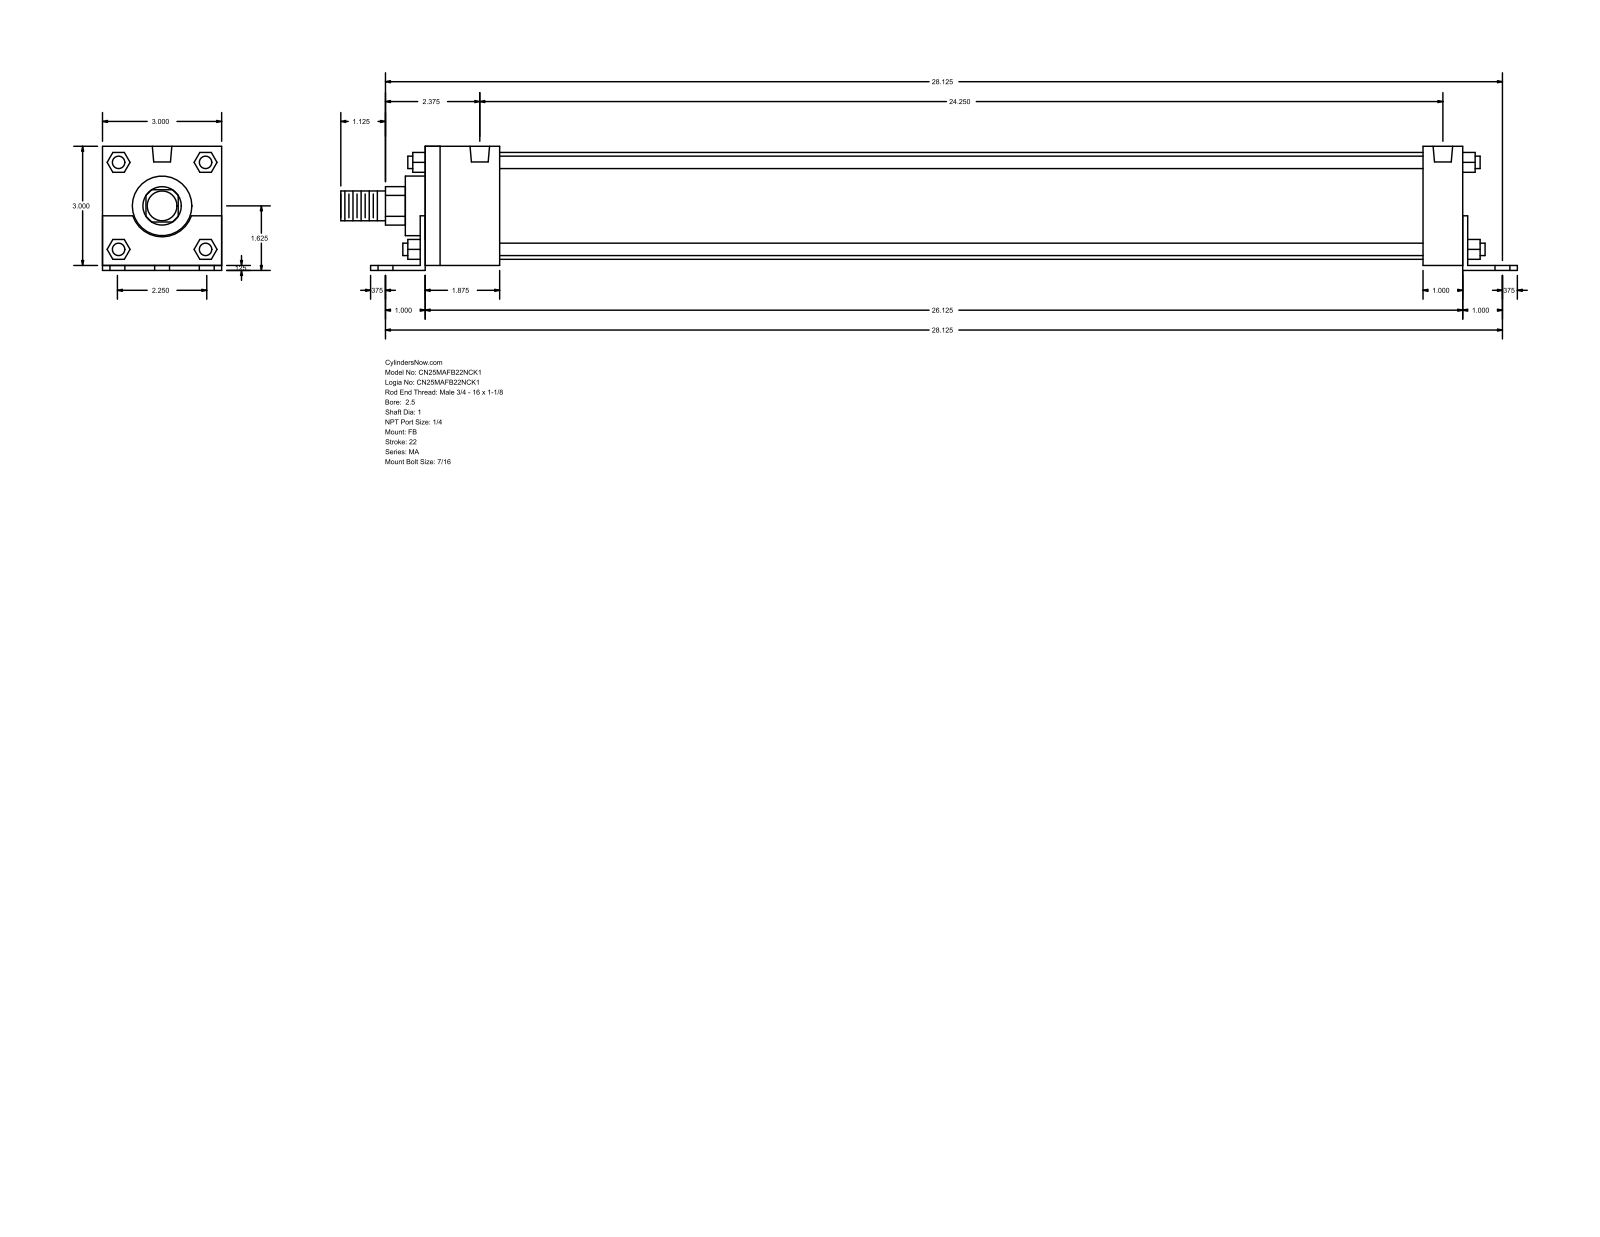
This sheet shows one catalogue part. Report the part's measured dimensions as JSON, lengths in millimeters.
{"part_name": "MA_FB__0250_1", "step_written_by": "GSSL Pune (CONFIG_CONTROL_DESIGN)", "units": "millimeters", "bodies": {"solids": 0, "faces": 140, "planar": 105, "cylindrical": 35, "other": 0}, "overall_size": [752.48, 79.38, 76.2], "round_holes": [[11.11, 6], [7.94, 4], [12.49, 2]], "round_bosses_or_shafts": [[7.94, 4], [68.33, 1], [38.1, 1], [25.4, 1], [19.05, 1]], "partial_cylinders_radius": [[12.29, 1], [19.81, 1]], "face_to_face_distances": [76.2, 3.17, 79.37, 666.75, 663.58, 12.7, 28.57, 25.4, 50.8, 47.63], "hole_center_spacings": [28.57, 714.95, 714.38, 47.63, 57.14, 66.75, 615.94, 654.67]}
